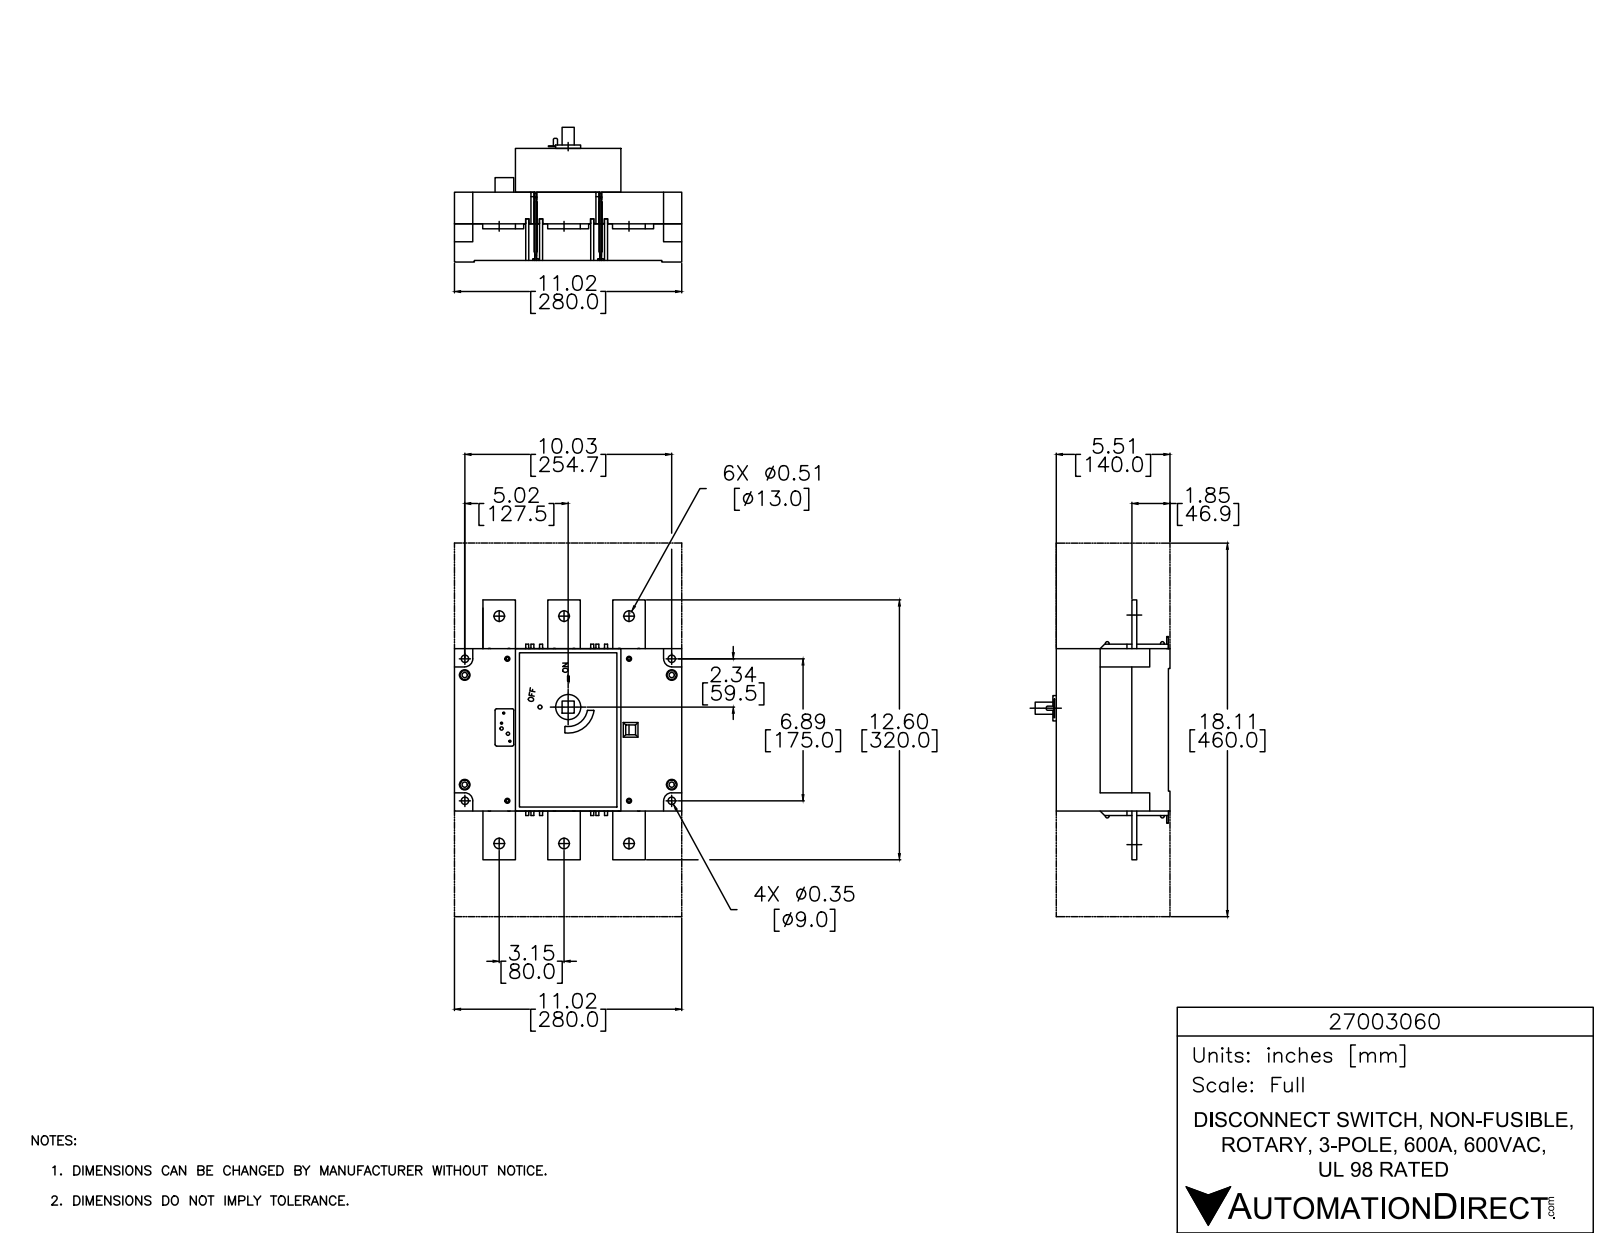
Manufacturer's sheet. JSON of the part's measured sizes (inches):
{"part_name": "27003060", "step_written_by": "SolidWorks 2015 (AUTOMOTIVE_DESIGN)", "units": "inches", "bodies": {"solids": 5, "faces": 385, "planar": 317, "cylindrical": 36, "other": 32}, "overall_size": [13.055, 11.024, 6.555], "volume_in3": 372.6, "surface_area_in2": 499.8, "round_holes": [[0.512, 6], [0.354, 4], [0.157, 1]], "round_bosses_or_shafts": [[0.201, 1], [0.039, 1]], "partial_cylinders_radius": [[0.472, 4], [0.61, 1], [0.945, 1], [1.26, 1]], "face_to_face_distances": [0.079, 3.15, 3.307, 7.874, 3.976, 2.087, 3.898, 7.126, 7.047, 5.394], "hole_center_spacings": [3.15, 10.71, 10.236, 2.366, 2.659, 5.105, 5.478, 5.539]}
